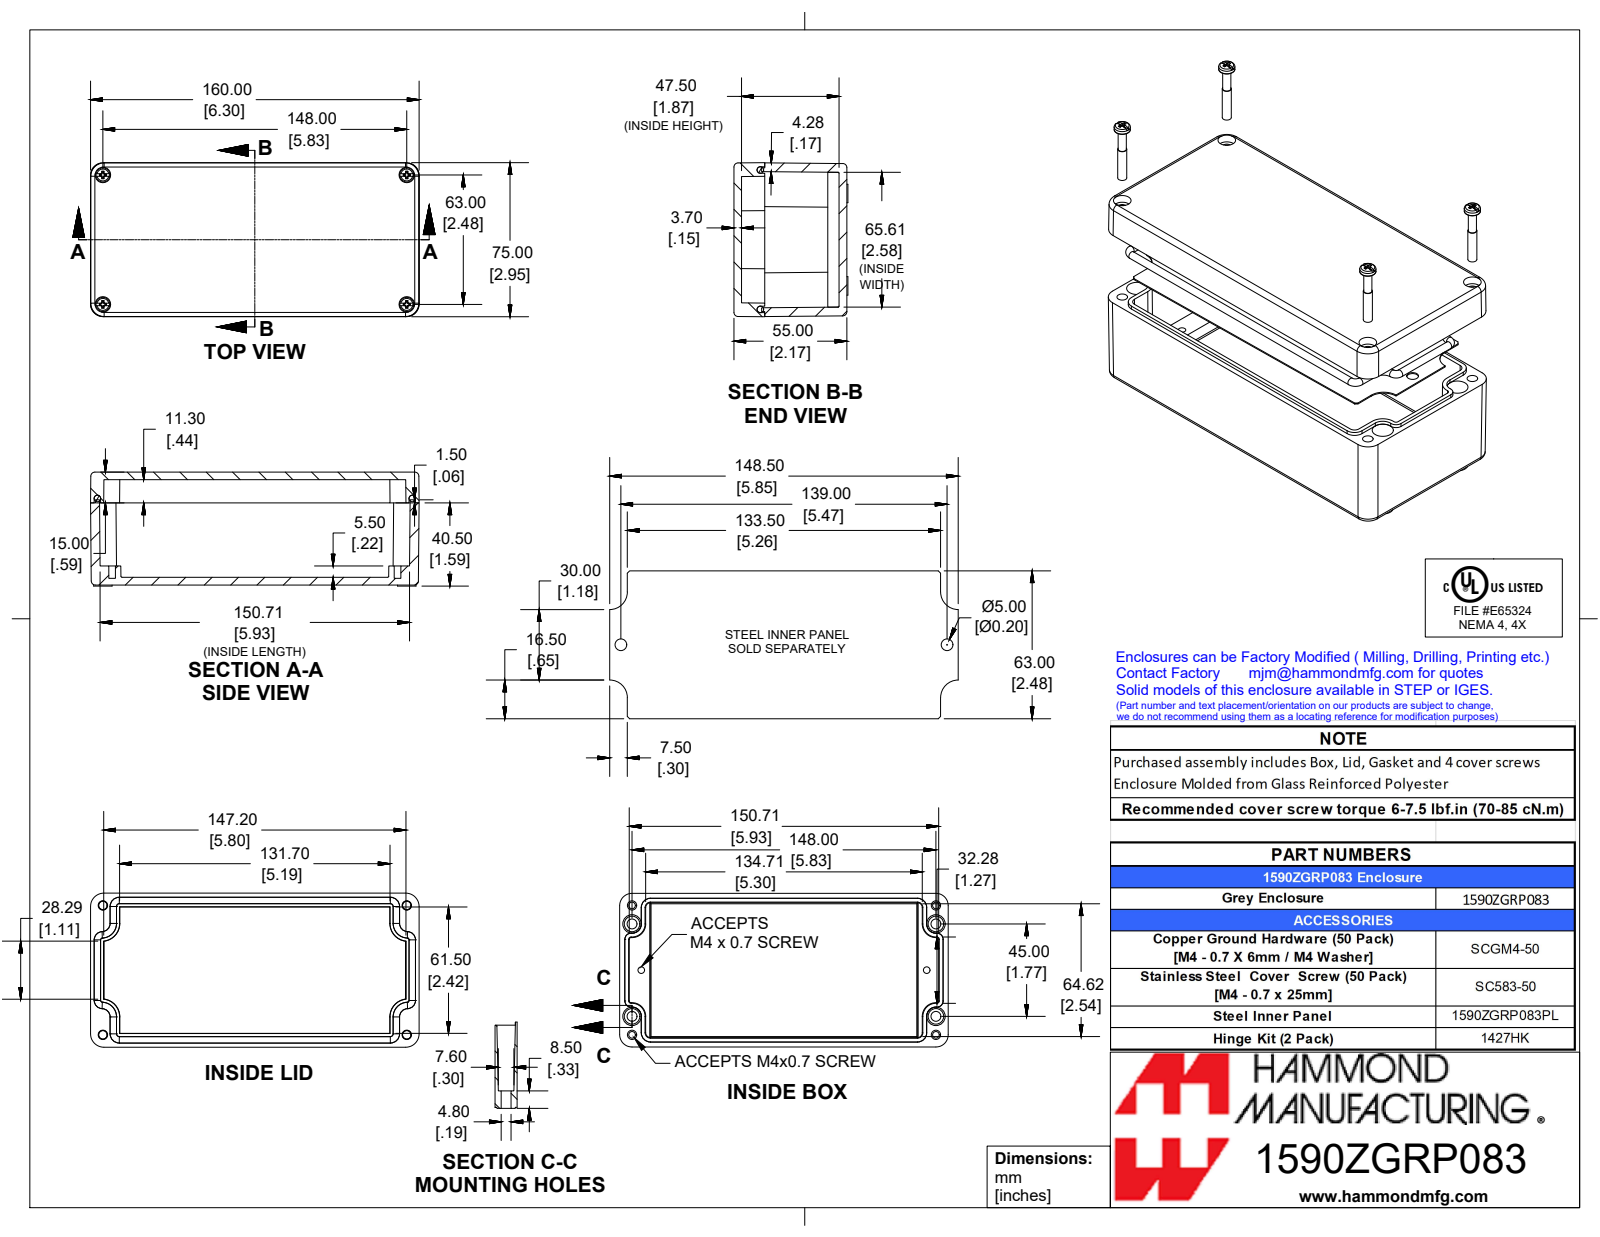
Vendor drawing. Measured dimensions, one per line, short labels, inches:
name: 1590ZGRP083
written by: SolidWorks 2019 (CONFIG_CONTROL_DESIGN)
unit: in
bodies: 8 solids, 428 faces (220 planar, 80 cylindrical, 128 other)
size: 6.299 × 2.953 × 2.185
volume: 13.08 in³; area: 192.9 in²
holes: 6× ⌀0.128, 4× ⌀0.161, 4× ⌀0.177, 4× ⌀0.189, 4× ⌀0.295, 2× ⌀0.197
bosses: 7× ⌀0.126, 4× ⌀0.354, 4× ⌀0.272, 4× ⌀0.152, 4× ⌀0.137
rounds: 8× R0.079, 6× R0.061, 4× R0.02, 4× R0.236, 4× R0.256, 4× R0.295
face distances: 2.165, 0.386, 0.169, 0.366, 1.799, 0.02, 1.634, 1.78, 1.654, 2.02
hole spacings: 0.354, 0.904, 1.253, 2.126, 5.719, 5.784, 5.827, 5.837
